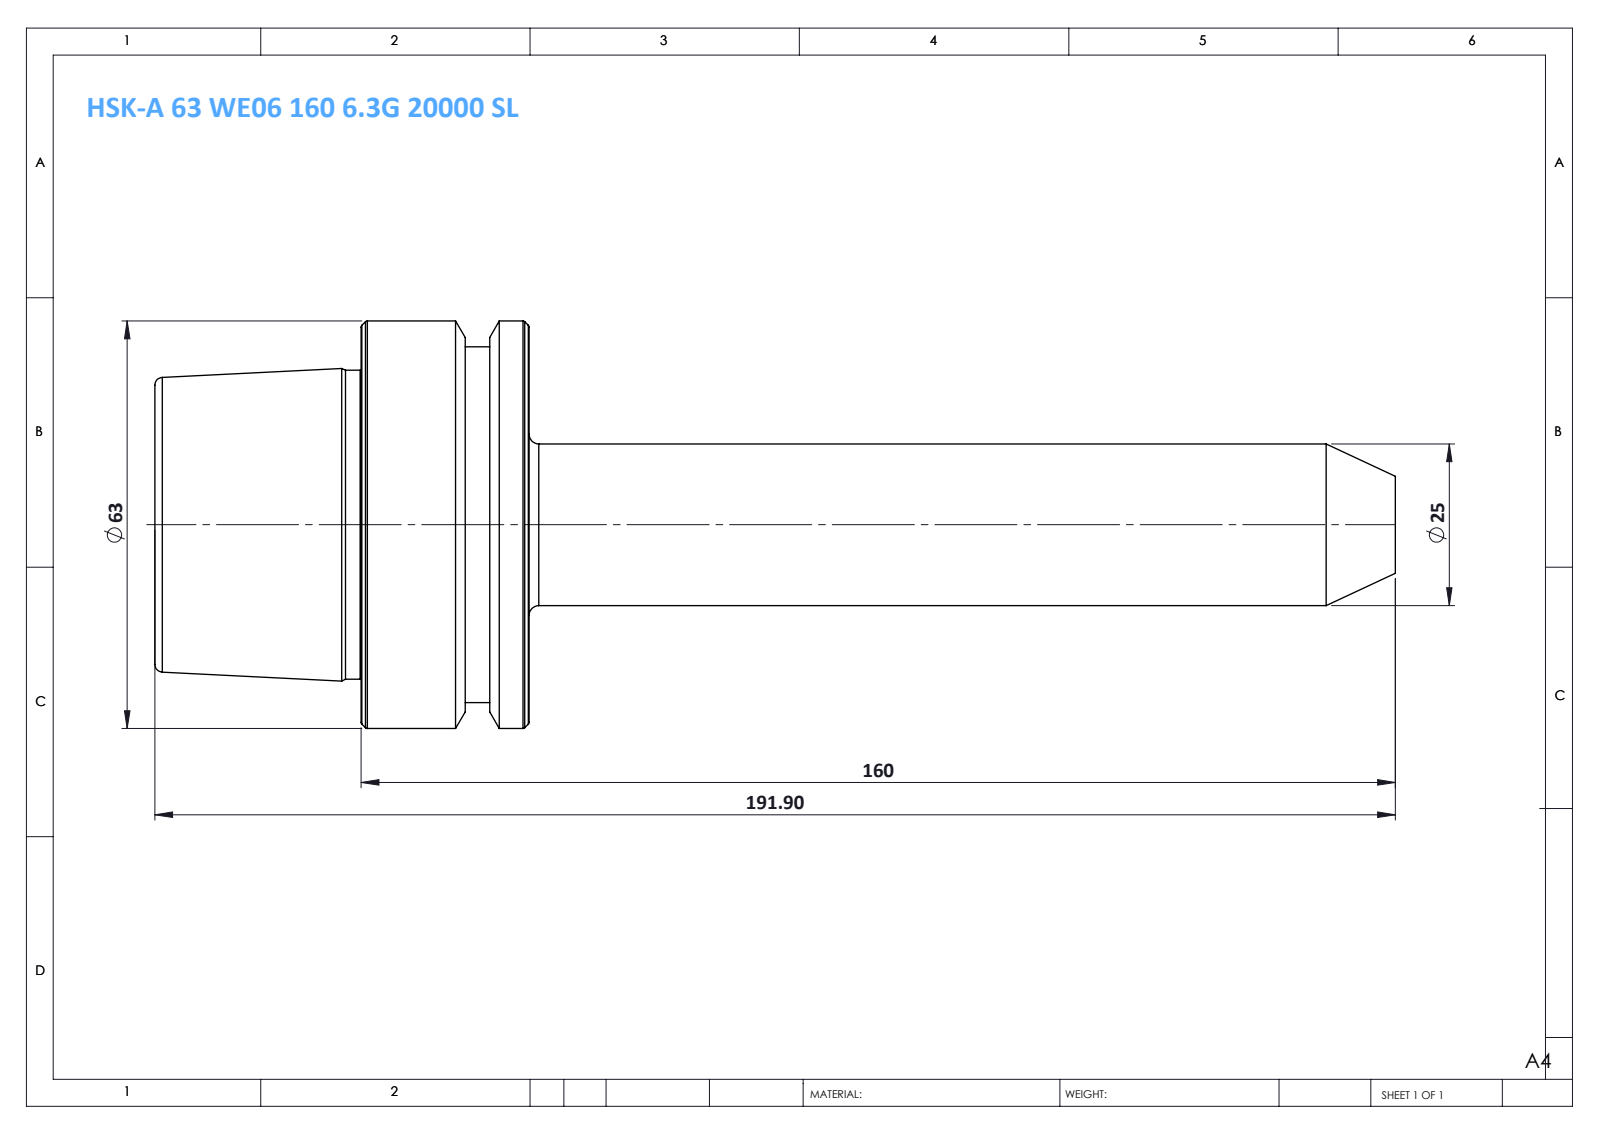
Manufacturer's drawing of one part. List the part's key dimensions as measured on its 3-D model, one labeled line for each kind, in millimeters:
Part name (STEP PRODUCT): HSK-A 63 WE06 160 6.3G 20000 SL
STEP written by: SolidWorks 2014 (CONFIG_CONTROL_DESIGN)
Units: millimetres
Bodies: 1 solid, 46 faces (6 planar, 10 cylindrical, 30 other)
Overall size (bounding box): 191.9 × 63 × 63
Volume: 196 563 mm³ · Surface area: 26 709 mm²
Round bosses / shafts (diameter × count): ⌀63 ×1, ⌀55 ×1, ⌀47.78 ×1, ⌀25 ×1
Main face-to-face distances: 57.9, 26, 31.9, 6.1, 19.9, 51.8, 9.9, 3.8, 16.1, 48
